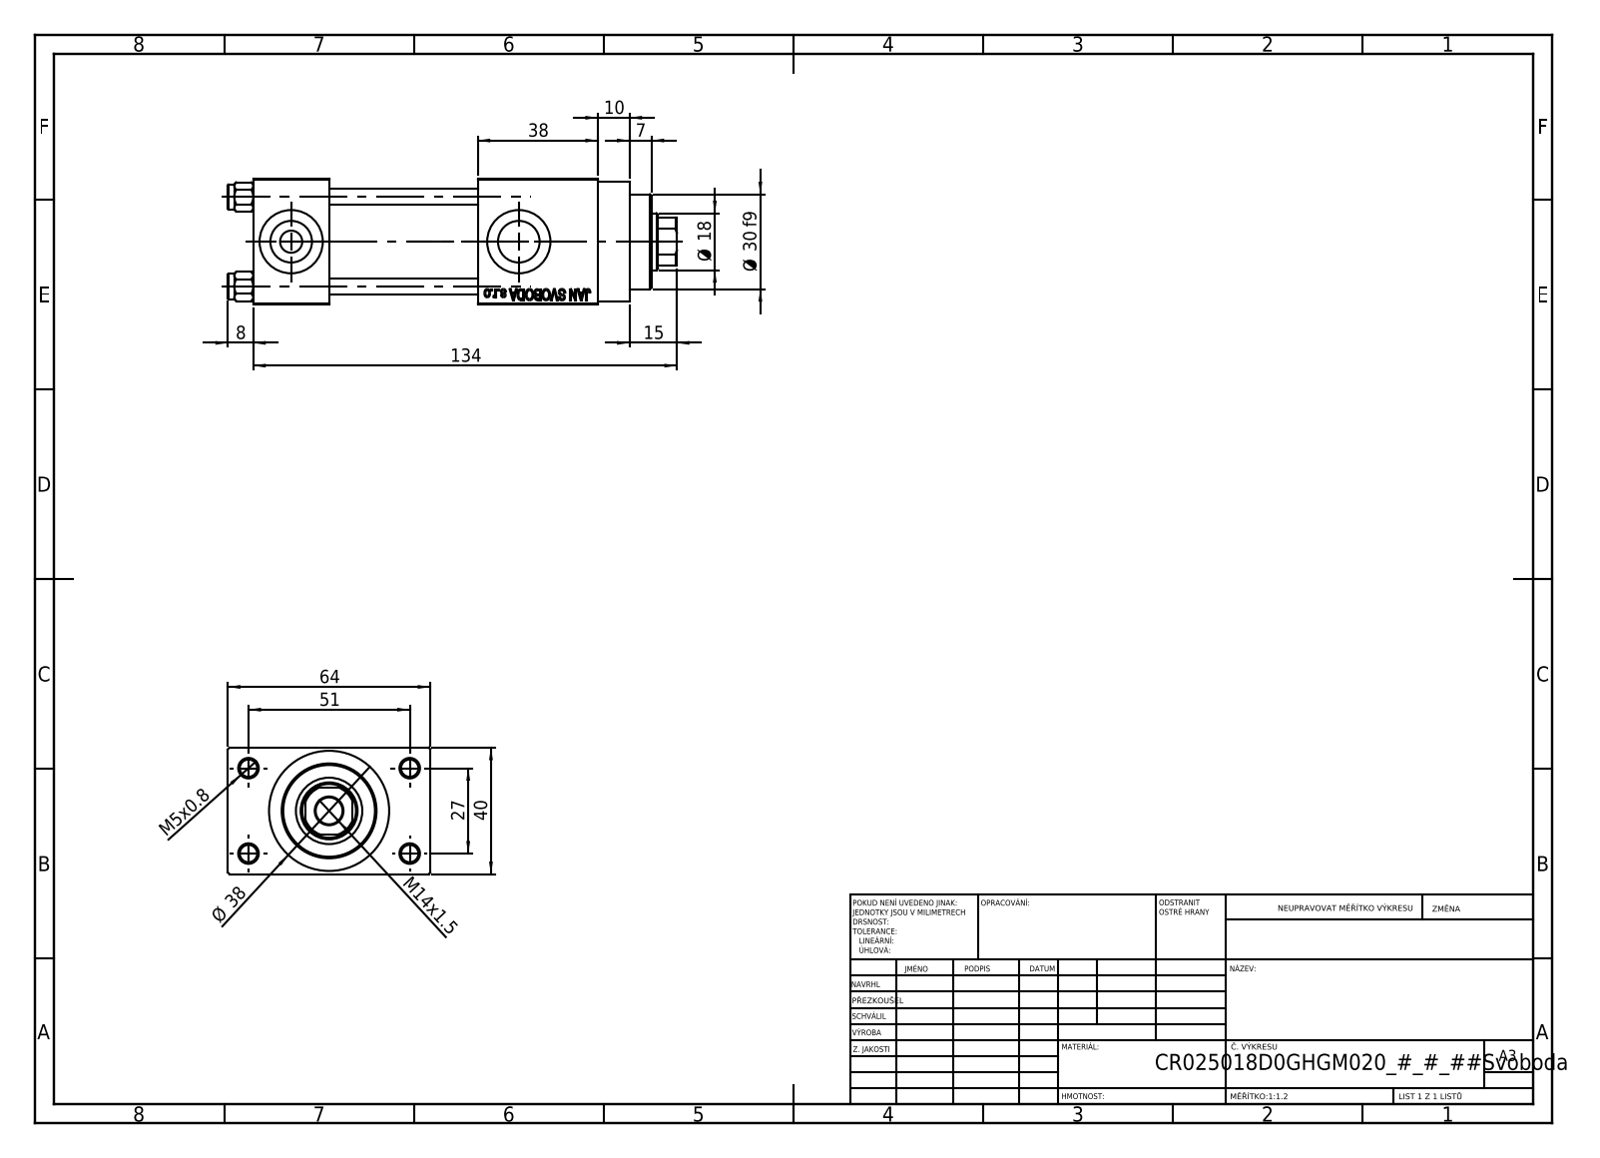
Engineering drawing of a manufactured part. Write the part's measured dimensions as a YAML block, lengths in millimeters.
part_name: "V215CR_VCP_D; V215CR_D_TYCINKA; V215CR_D_Body; V215_VC_A (+1 more)"
step_written_by: "SolidWorks 2019 (CONFIG_CONTROL_DESIGN)"
units: millimeters
bodies: {solids: 11, faces: 1099, planar: 495, cylindrical: 86, other: 518}
overall_size: [142, 64, 40]
volume: 179232
surface_area: 64709
round_holes:
  - {diameter: 5, count: 4}
  - {diameter: 5.5, count: 4}
  - {diameter: 20, count: 3}
  - {diameter: 7, count: 2}
  - {diameter: 13.16, count: 2}
  - {diameter: 8.5, count: 1}
  - {diameter: 18, count: 1}
  - {diameter: 21, count: 1}
  - {diameter: 25, count: 1}
  - {diameter: 30, count: 1}
round_bosses_or_shafts:
  - {diameter: 8, count: 4}
  - {diameter: 38, count: 1}
  - {diameter: 31, count: 1}
partial_cylinders:
  - {radius: 8.5, count: 1}
face_to_face_distances: [40, 12, 47, 24, 71, 52, 38, 109, 85, 64]
hole_center_spacings: [11.37, 20.01, 28.3, 28.85, 29.89, 39.66, 48.34, 27]
